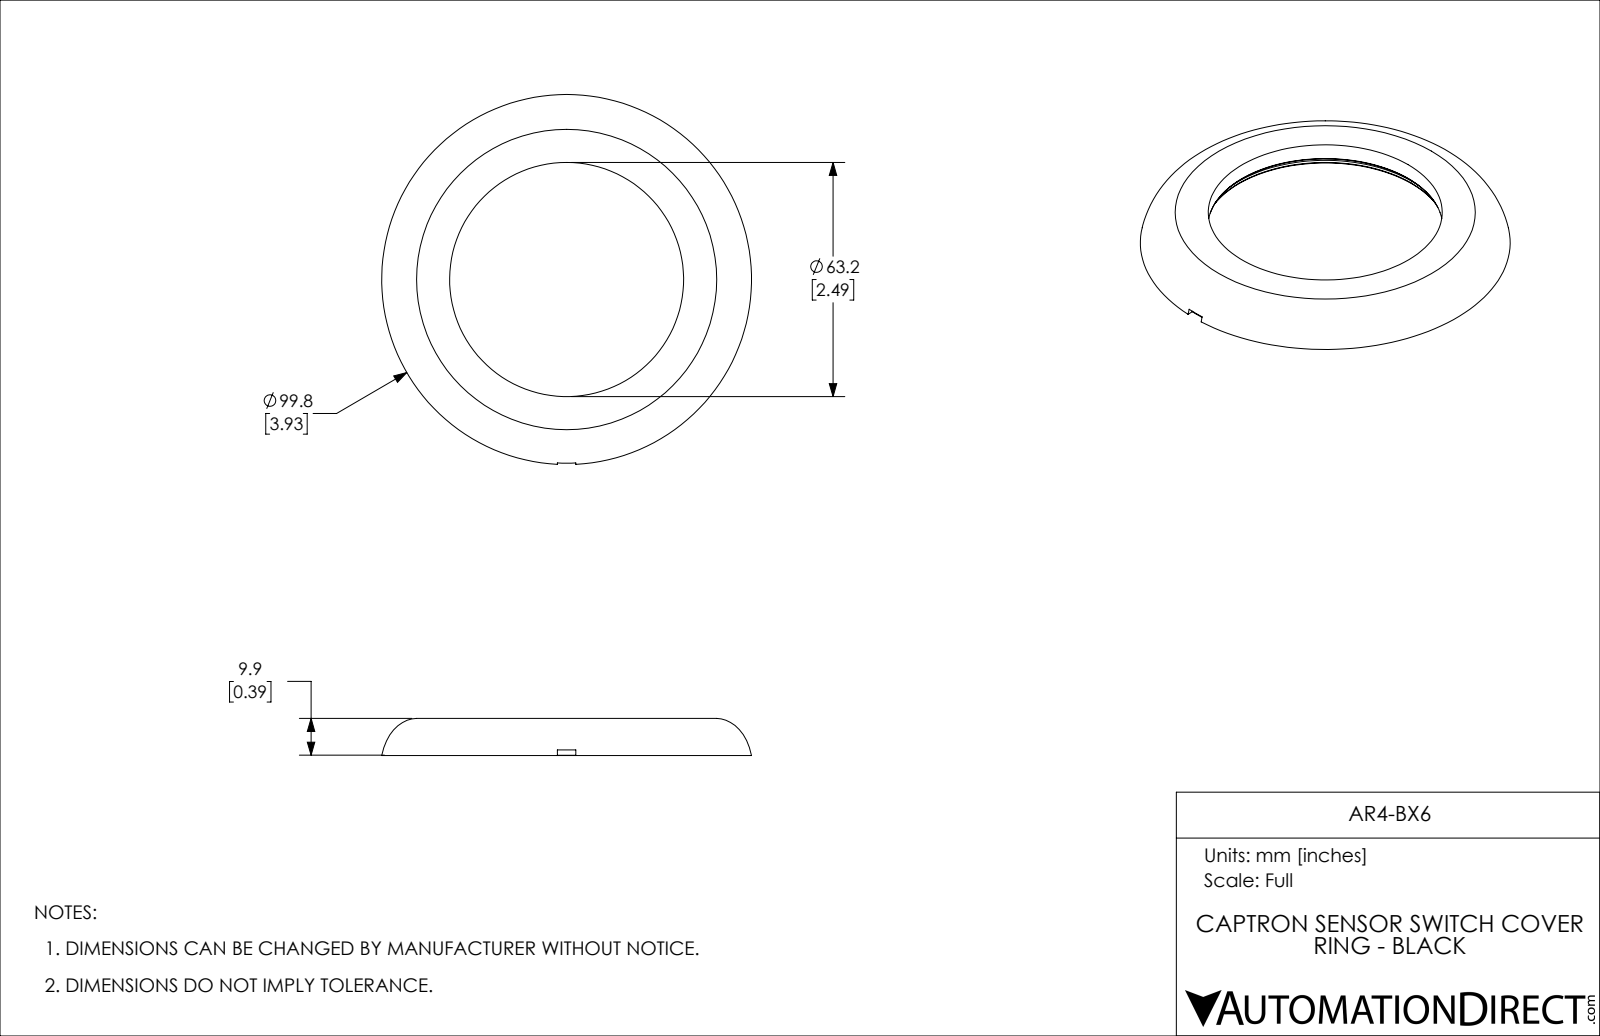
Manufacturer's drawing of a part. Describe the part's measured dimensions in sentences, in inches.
The part is named "AR4-BX6". Its 3-D file was written by "SolidWorks 2019 (CONFIG_CONTROL_DESIGN)". It is 1 solid with 49 faces: 7 planar, 4 cylindrical and 38 other. Overall it measures 3.929 by 3.927 by 0.394 inches. Its volume is 0.743 cubic inches and its surface area 22.88 square inches. Round holes: 1 of diameter 2.583, 1 of diameter 3.714. The main face-to-face distances are 0.079, 0.197, 0.276, 0.087, 0.11, 0.189, 0.059, 0.146, 0.256, 0.335.
